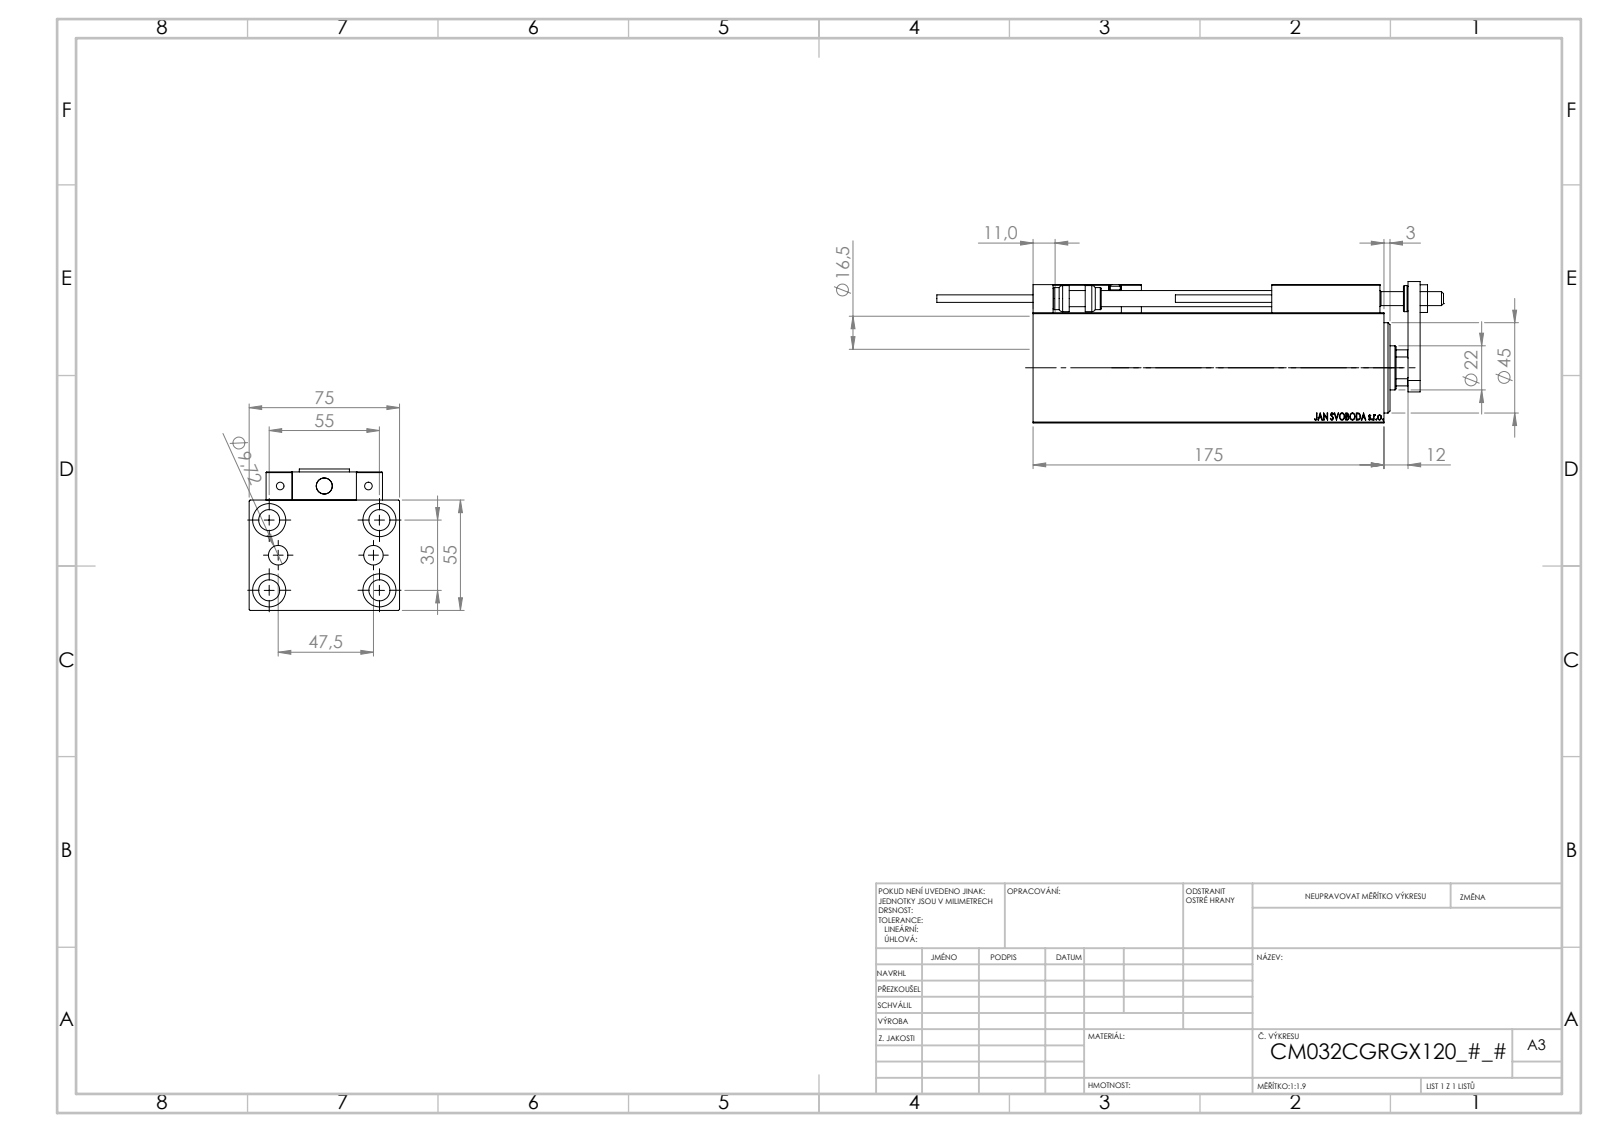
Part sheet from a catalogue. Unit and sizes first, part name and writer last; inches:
Units: inches
Overall size (bounding box): 9.949 × 2.953 × 2.776
Round holes (diameter × count): ⌀0.157 ×6, ⌀0.315 ×5, ⌀0.413 ×5, ⌀0.65 ×5, ⌀0.126 ×4, ⌀0.197 ×2, ⌀0.383 ×2, ⌀0.276 ×1, ⌀0.866 ×1, ⌀1.004 ×1, ⌀1.26 ×1, ⌀1.339 ×1
Round bosses / shafts (diameter × count): ⌀0.197 ×2, ⌀0.15 ×2, ⌀0.512 ×1, ⌀0.433 ×1
Partial cylindrical surfaces — rounded edges, fillets, slot ends (radius × count): R0.012 ×30, R0.118 ×2, R0.413 ×1
Main face-to-face distances: 2.165, 2.953, 0.551, 0.394, 2.717, 0.472, 0.197, 0.984, 0.709, 0.118
Hole centre spacings: 0.705, 1.283, 2.132, 0.448, 0.787, 0.935, 1.165, 1.169
Volume: 39.78 in³ · Surface area: 229.9 in²
Bodies: 23 solids, 1278 faces (560 planar, 184 cylindrical, 534 other)
Part name (STEP PRODUCT): ALLEN BOLT D5; V450CM_C_Body; Block; V450CM_VC_B (+7 more)
STEP written by: SolidWorks 2019 (CONFIG_CONTROL_DESIGN)
